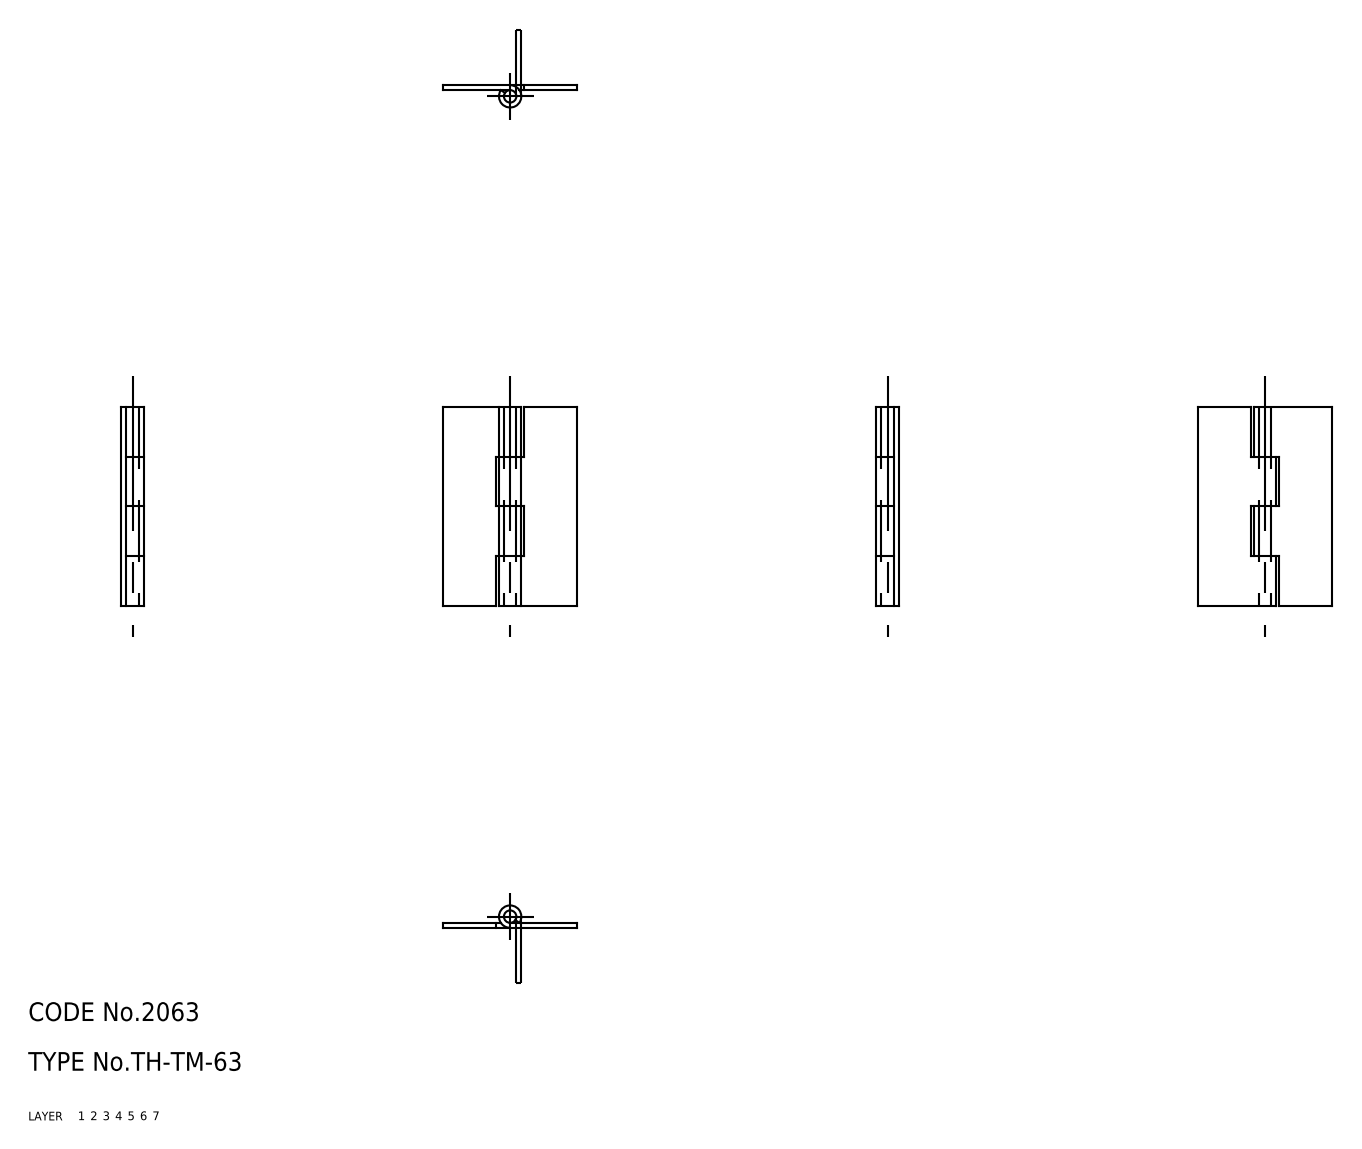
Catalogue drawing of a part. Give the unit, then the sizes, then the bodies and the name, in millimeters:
Units: millimetres
Overall size (bounding box): 32 × 21.5 × 3.6
Volume: 782 mm³ · Surface area: 2 103 mm²
Bodies: 3 solids, 36 faces (0 planar, 0 cylindrical, 36 other)
Part name (STEP PRODUCT): hinge piece_B; hinge piece_A; shaft; TH_TM_63_24678_36
STEP written by: CADfix (AUTOMOTIVE_DESIGN)
